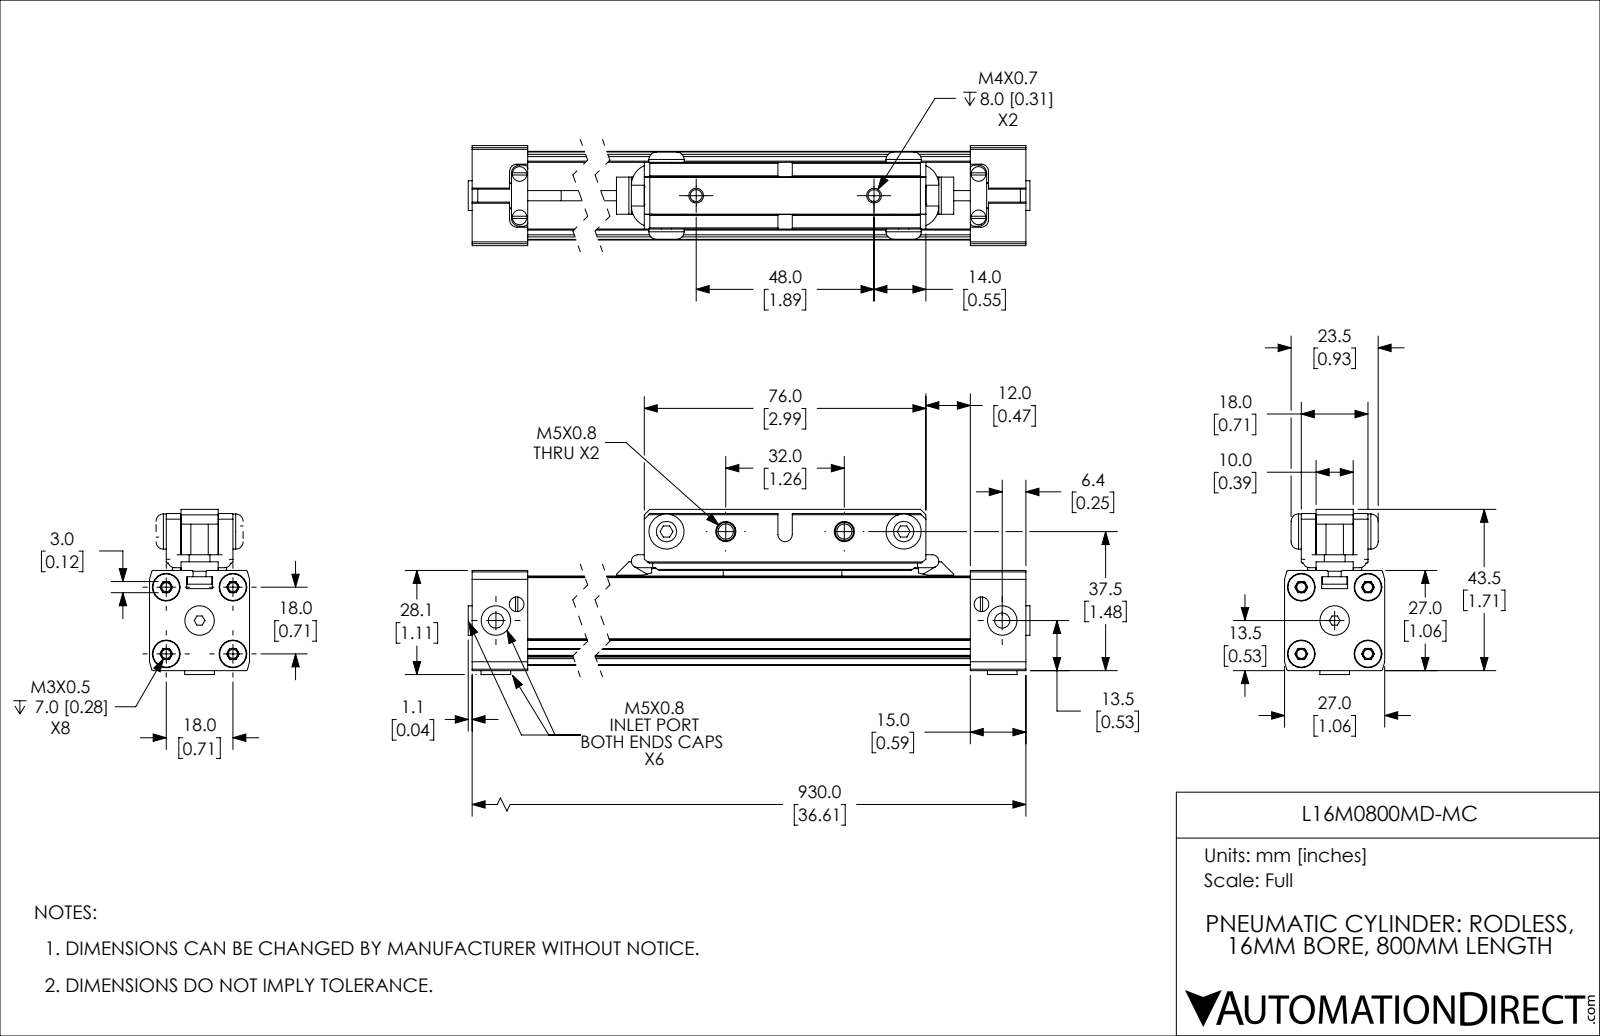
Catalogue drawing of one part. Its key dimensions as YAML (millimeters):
part_name: "L16M0800MD-MC_BODY; L16M0800MD-MC; L16M0800MD-MC_PISTON"
step_written_by: "SolidWorks 2019 (CONFIG_CONTROL_DESIGN)"
units: millimeters
bodies: {solids: 13, faces: 827, planar: 435, cylindrical: 284, other: 108}
overall_size: [932.15, 44.57, 27]
volume: 356839
surface_area: 184687
round_holes:
  - {diameter: 4.13, count: 9}
  - {diameter: 4, count: 6}
  - {diameter: 8, count: 5}
  - {diameter: 2.46, count: 4}
  - {diameter: 5.5, count: 4}
  - {diameter: 7.5, count: 4}
  - {diameter: 3.24, count: 2}
  - {diameter: 16.1, count: 1}
round_bosses_or_shafts:
  - {diameter: 7.2, count: 4}
  - {diameter: 3.5, count: 4}
  - {diameter: 5, count: 3}
  - {diameter: 3.8, count: 3}
  - {diameter: 9.5, count: 2}
  - {diameter: 16, count: 1}
partial_cylinders:
  - {radius: 0.3, count: 22}
  - {radius: 0.5, count: 14}
  - {radius: 0.25, count: 8}
  - {radius: 0.62, count: 6}
  - {radius: 1, count: 6}
  - {radius: 0.2, count: 4}
  - {radius: 0.6, count: 4}
  - {radius: 2, count: 4}
face_to_face_distances: [23.9, 24, 10.58, 13.32, 2.74, 20.95, 2.65, 4.3, 2.95, 7.63]
hole_center_spacings: [8.67, 12.73, 18, 910.82, 48, 7.12, 11.7, 11.91]
